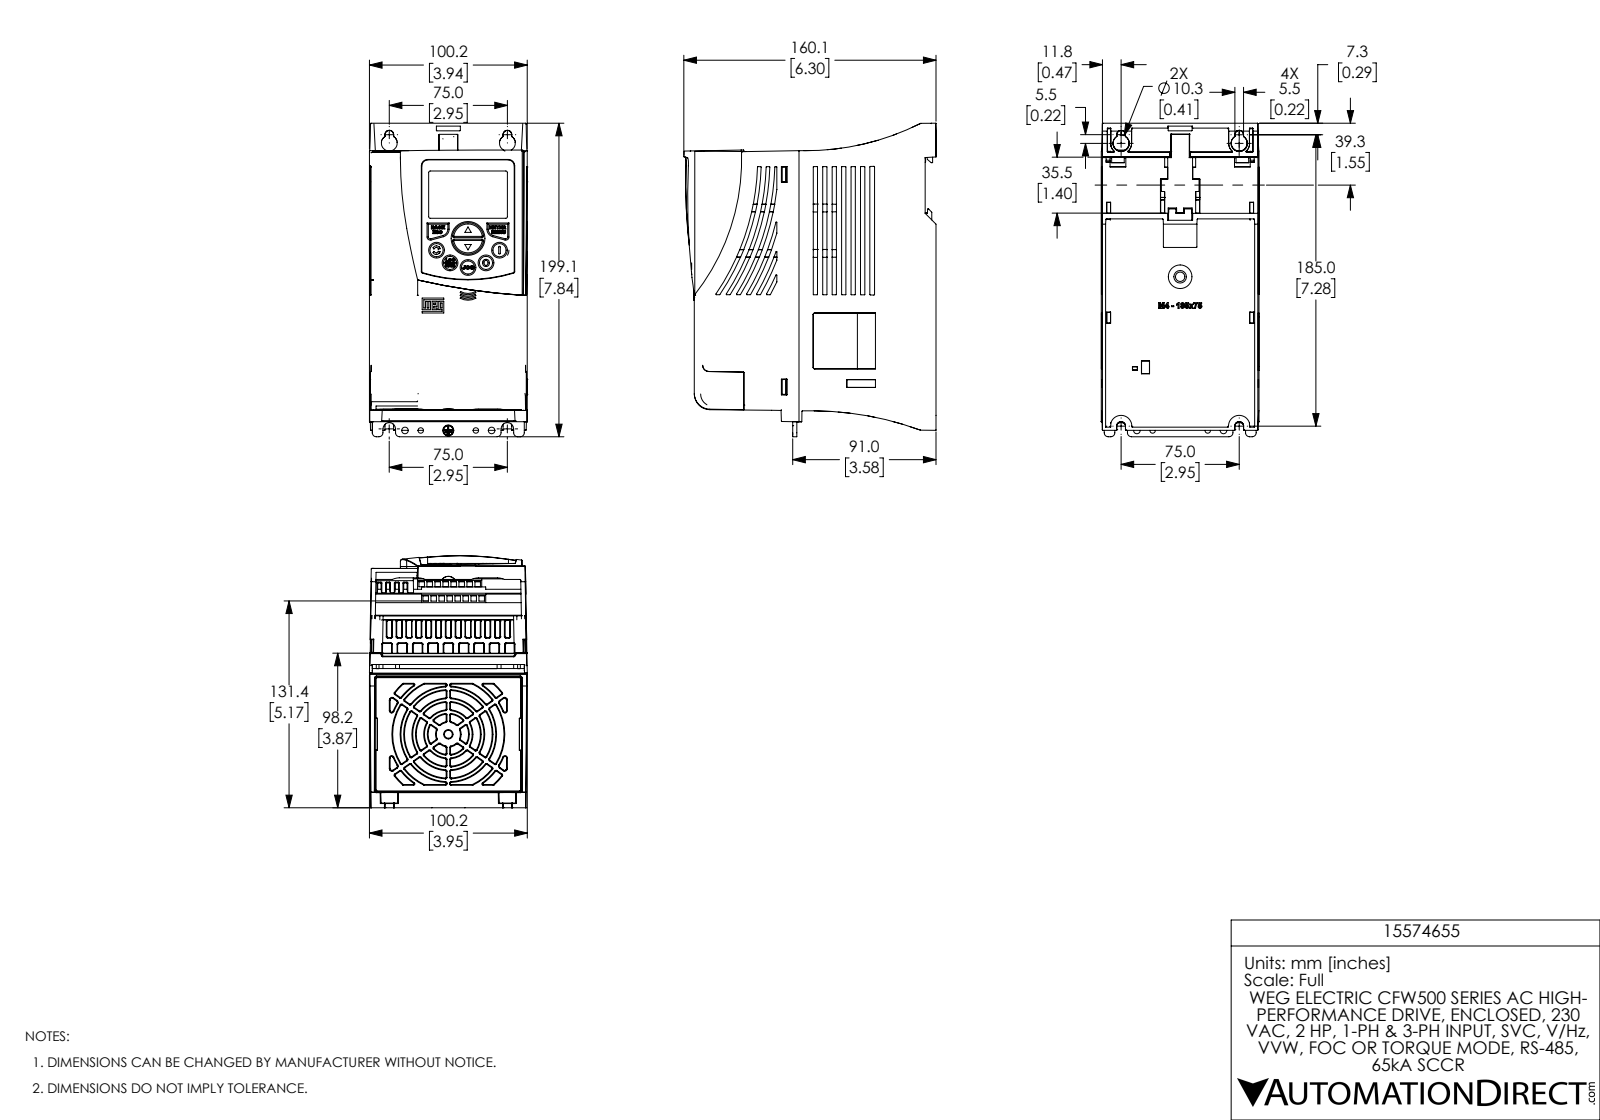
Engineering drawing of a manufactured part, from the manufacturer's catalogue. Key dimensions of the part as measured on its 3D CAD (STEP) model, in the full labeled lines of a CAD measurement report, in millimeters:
Part name (STEP PRODUCT): CFW50X_FRAME_B_NEMA1_PAR fStep r2b red1b ext3C b4D
STEP written by: SolidWorks 2017 (AUTOMOTIVE_DESIGN)
Units: millimetres
Bodies: 3 solids, 4016 faces (1691 planar, 835 cylindrical, 1490 other)
Overall size (bounding box): 199.1 × 160.1 × 100.2
Volume: 2 356 000 mm³ · Surface area: 170 800 mm²
Round holes (diameter × count): ⌀10 ×3, ⌀3.5 ×2, ⌀4.2 ×2, ⌀9.8 ×2, ⌀20 ×1, ⌀21.5 ×1
Round bosses / shafts (diameter × count): ⌀10 ×2
Partial cylindrical surfaces — rounded edges, fillets, slot ends (radius × count): R0.3 ×331, R0.2 ×88, R0.5 ×36, R1 ×18, R2.5 ×8, R10 ×6, R4 ×4, R2 ×3
Main face-to-face distances: 1.3, 3.1, 143.5, 146.6, 1.5, 145.1, 1.6, 0.9, 141.3, 2.2
Hole centre spacings: 22.8, 10, 11.8, 11.8, 19.3, 21.4, 32.4, 45
